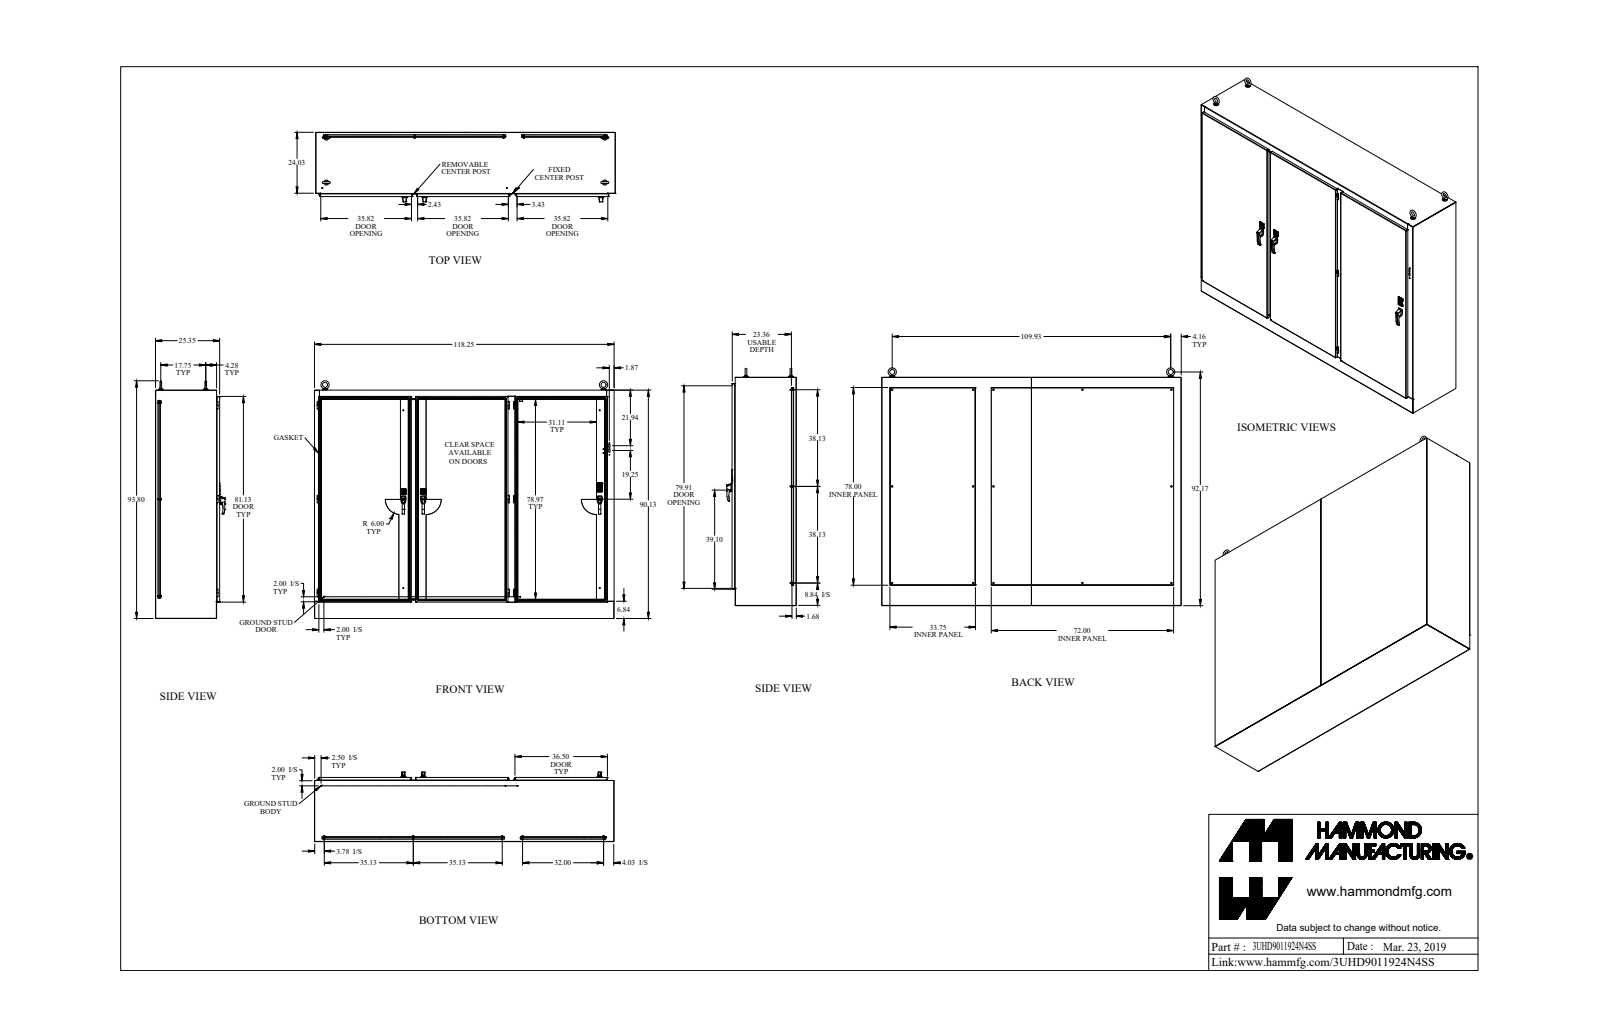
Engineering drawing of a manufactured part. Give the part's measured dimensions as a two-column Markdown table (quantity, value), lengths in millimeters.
| quantity | value |
| --- | --- |
| part name | 3UHD9011924N4SS |
| STEP written by | SolidWorks 2018 (AUTOMOTIVE_DESIGN) |
| units | millimeters |
| bodies | 310 solids, 4550 faces (2764 planar, 1295 cylindrical, 491 other) |
| overall size | 3003.6 × 2382.5 × 697.6 |
| volume | 69 890 000 mm³ |
| surface area | 61 900 000 mm² |
| round holes (diameter × count) | 6.4 × 27, 5 × 20, 7.8 × 14, 7.1 × 10, 8 × 9, 8.9 × 9, 11.3 × 9, 22.2 × 8, 4 × 6, 5.1 × 6, 6.5 × 6, 6.8 × 6 |
| round bosses / shafts (diameter × count) | 25.4 × 22, 6.4 × 17, 9.5 × 15, 16.5 × 14, 8.4 × 14, 6.2 × 10, 15.9 × 8, 12.3 × 7 |
| partial cylindrical surfaces (radius × count) | 3.2 × 71, 0.4 × 48, 1.5 × 42, 1.2 × 41, 3.6 × 41, 12.7 × 40, 6.4 × 32, 4.7 × 20 |
| main face-to-face distances | 2.4, 2, 595.9, 644.3, 641.9, 642.3, 639.9, 48.4, 46, 593.9 |
| hole center spacings | 1968.5, 54, 199.9, 450.9, 1768.6, 1936.8, 2792.3, 2792.8 |
